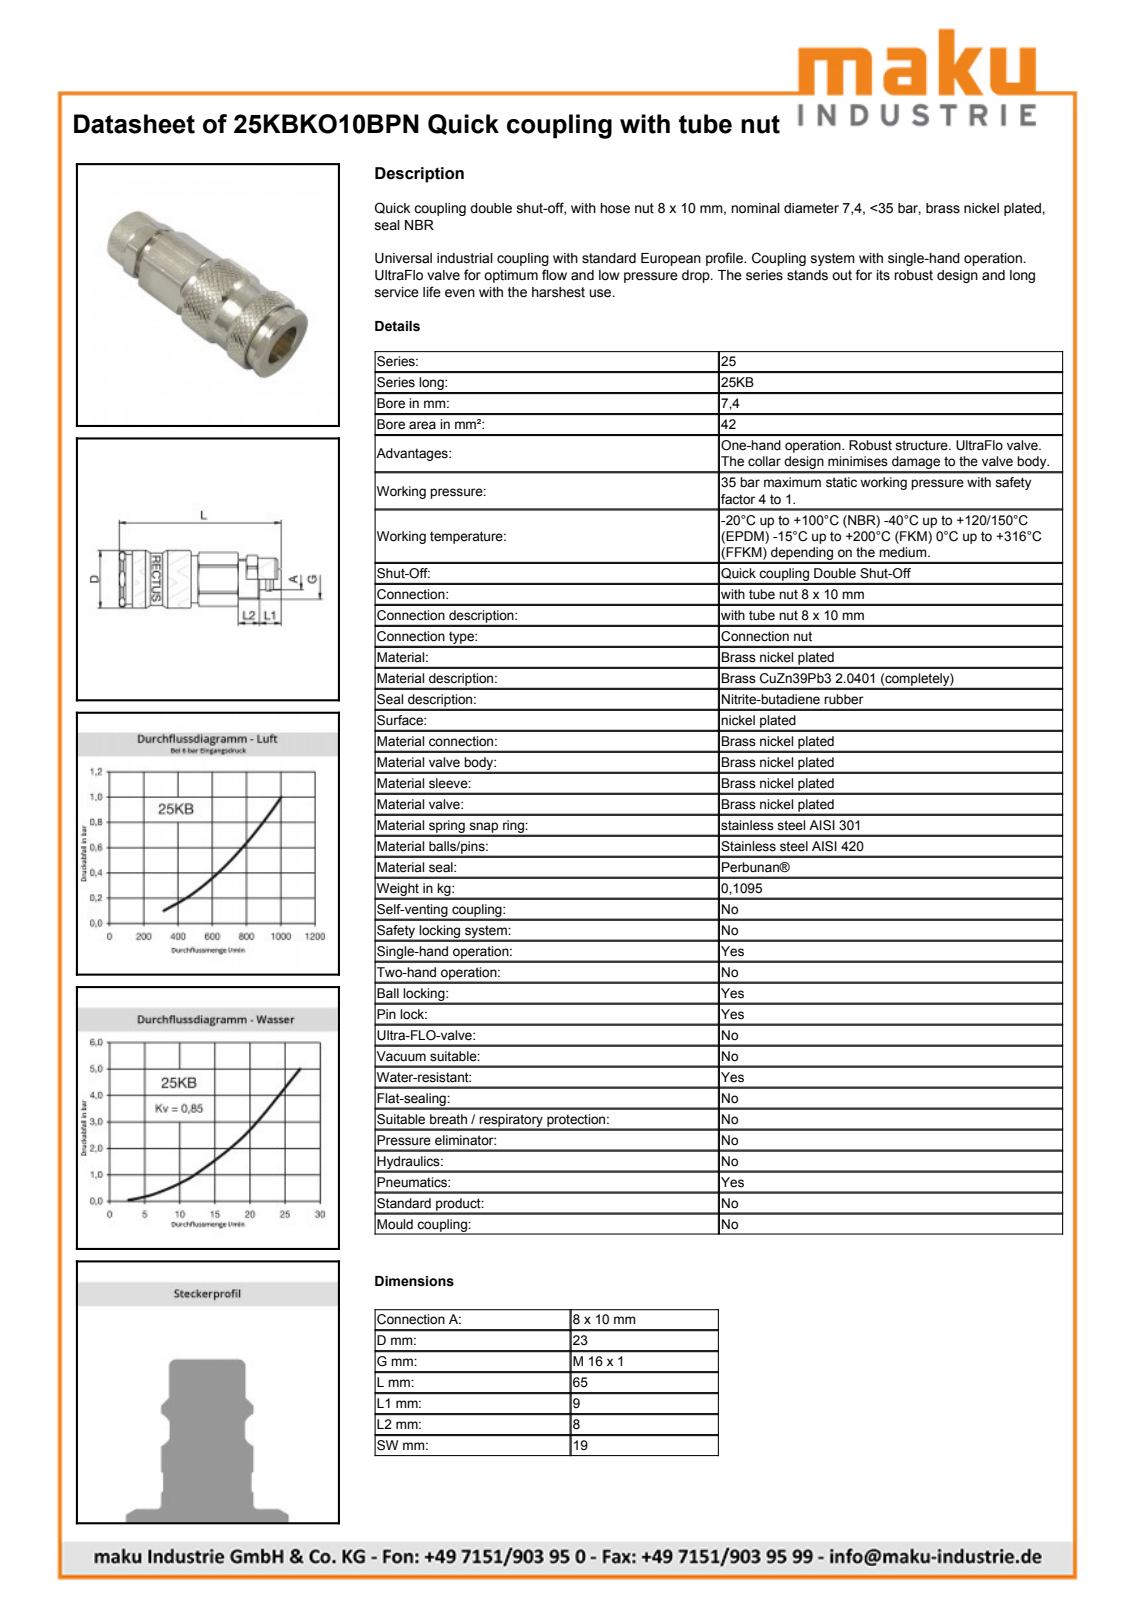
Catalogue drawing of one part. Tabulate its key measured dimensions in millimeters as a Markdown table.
| quantity | value |
| --- | --- |
| part name | D109864 |
| STEP written by | Autodesk Inventor 2013 (AUTOMOTIVE_DESIGN) |
| units | millimeters |
| bodies | 2 solids, 606 faces (227 planar, 85 cylindrical, 294 other) |
| overall size | 64.5 × 23.15 × 23.15 |
| volume | 18 397 mm³ |
| surface area | 9 140 mm² |
| round holes (diameter × count) | 10.2 × 1, 15.1 × 1, 15.46 × 1, 15.6 × 1, 17.25 × 1, 19.35 × 1, 20.05 × 1 |
| round bosses / shafts (diameter × count) | 23.15 × 1, 21 × 1, 20 × 1, 18.95 × 1, 17 × 1, 16 × 1, 15.3 × 1, 15 × 1 |
| partial cylindrical surfaces (radius × count) | 9.57 × 1, 10.4 × 1, 10.7 × 1, 11 × 1 |
| main face-to-face distances | 19, 17, 55.9, 12.9, 60.4, 4.5, 62.4, 6.5, 2, 47.5 |
